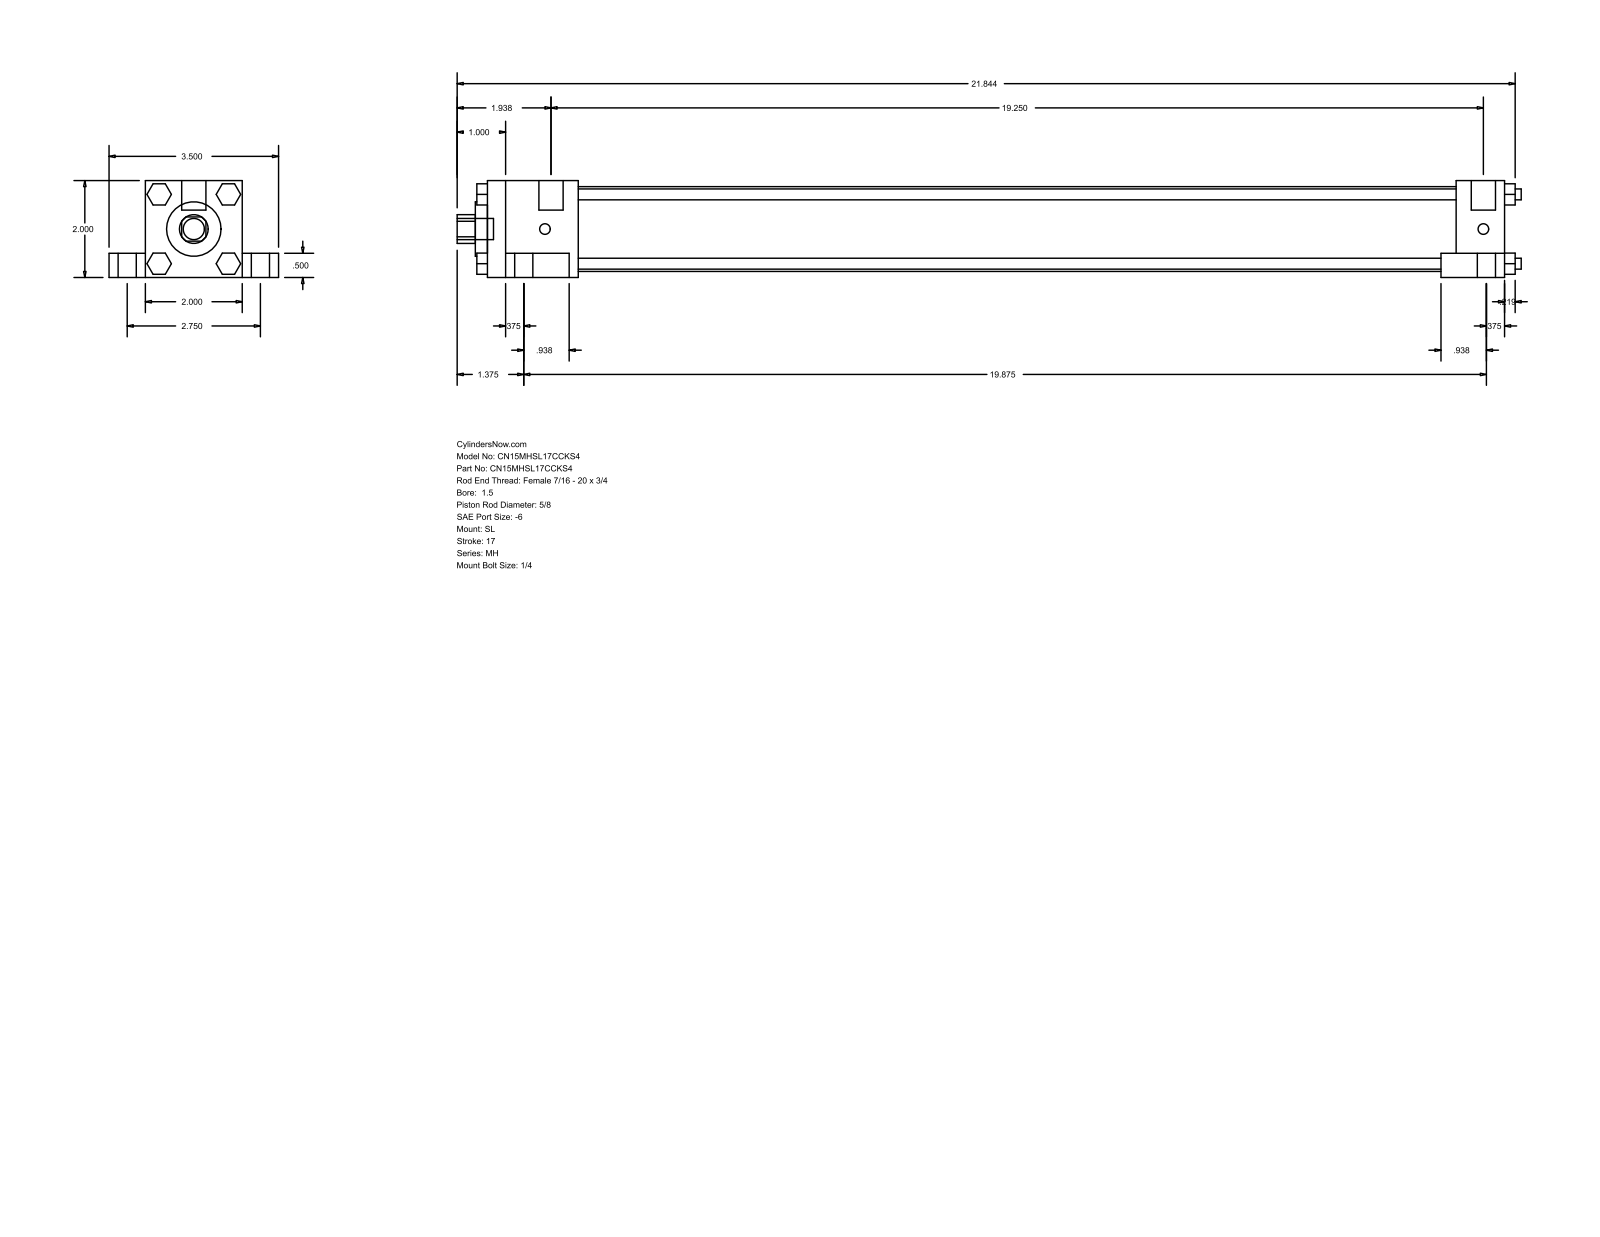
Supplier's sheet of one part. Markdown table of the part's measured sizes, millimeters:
| quantity | value |
| --- | --- |
| part name | MH_SL__0150_0.625 |
| STEP written by | GSSL Pune (CONFIG_CONTROL_DESIGN) |
| units | millimeters |
| bodies | 0 solids, 148 faces (112 planar, 36 cylindrical, 0 other) |
| overall size | 558.01 × 88.9 × 50.8 |
| round holes (diameter × count) | 15.88 × 1, 28.57 × 1, 44.45 × 1 |
| round bosses / shafts (diameter × count) | 15.88 × 4, 9.53 × 4, 5.71 × 4, 5.56 × 4, 12.7 × 2, 11.11 × 1 |
| partial cylindrical surfaces (radius × count) | 7.54 × 1 |
| main face-to-face distances | 50.8, 38.1, 19.05, 12.7, 69.85, 533.39, 9.52, 508, 25.39, 47.62 |
